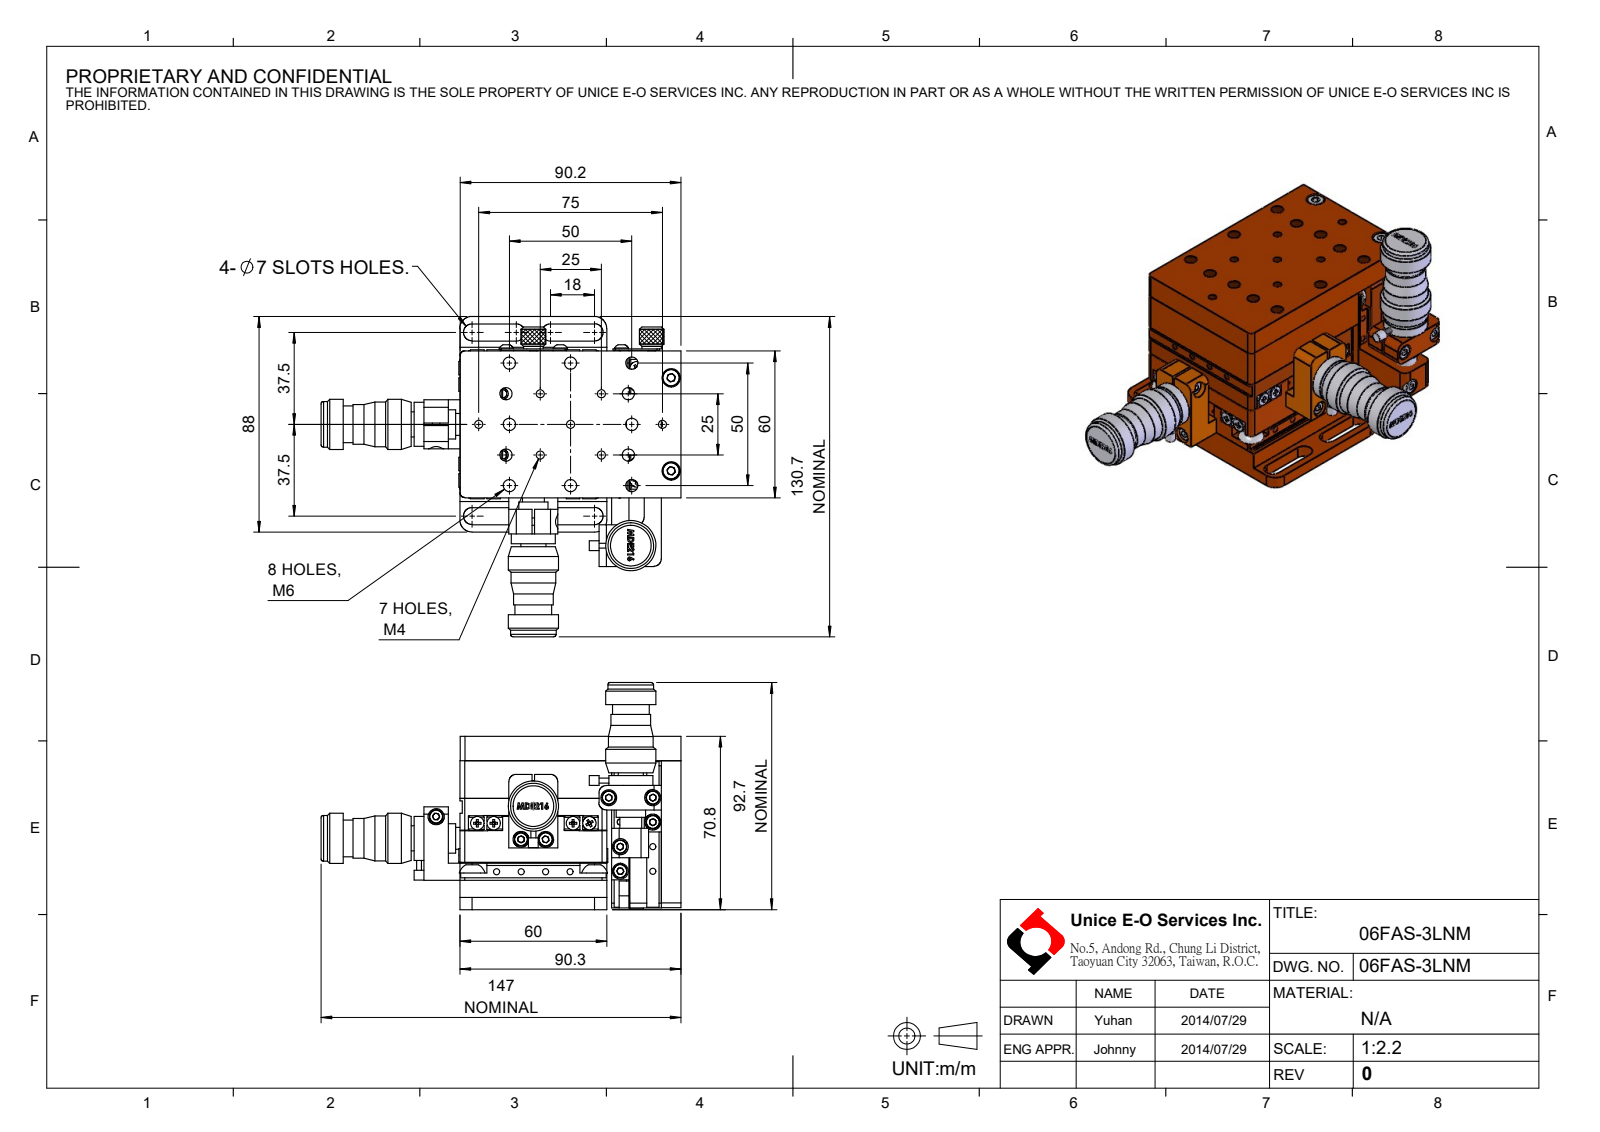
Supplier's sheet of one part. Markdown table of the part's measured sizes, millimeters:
| quantity | value |
| --- | --- |
| part name | 06FAS-3LNM |
| STEP written by | SolidWorks 2016 (CONFIG_CONTROL_DESIGN) |
| units | millimeters |
| bodies | 99 solids, 5170 faces (1847 planar, 1407 cylindrical, 1916 other) |
| overall size | 147 × 130.7 × 92.7 |
| volume | 400 015 mm³ |
| surface area | 171 453 mm² |
| round holes (diameter × count) | 2.05 × 60, 5 × 60, 2.5 × 41, 3 × 36, 6.5 × 19, 3.3 × 17, 3.4 × 11, 4.5 × 10, 8 × 8, 3.2 × 4, 3.5 × 4, 3.1 × 3 |
| round bosses / shafts (diameter × count) | 3 × 31, 5.5 × 25, 6 × 10, 4 × 9, 7 × 6, 5.7 × 4, 20.5 × 3, 18.64 × 3 |
| partial cylindrical surfaces (radius × count) | 2 × 12, 3 × 12, 3.5 × 8, 6 × 8, 1.75 × 4, 5 × 4 |
| main face-to-face distances | 7, 13.1, 20.3, 13.2, 33.4, 15.4, 60, 6, 6.1, 48.8 |
| hole center spacings | 20, 10, 19.45, 29.12, 31.91, 38.58, 49.58, 51.08 |
